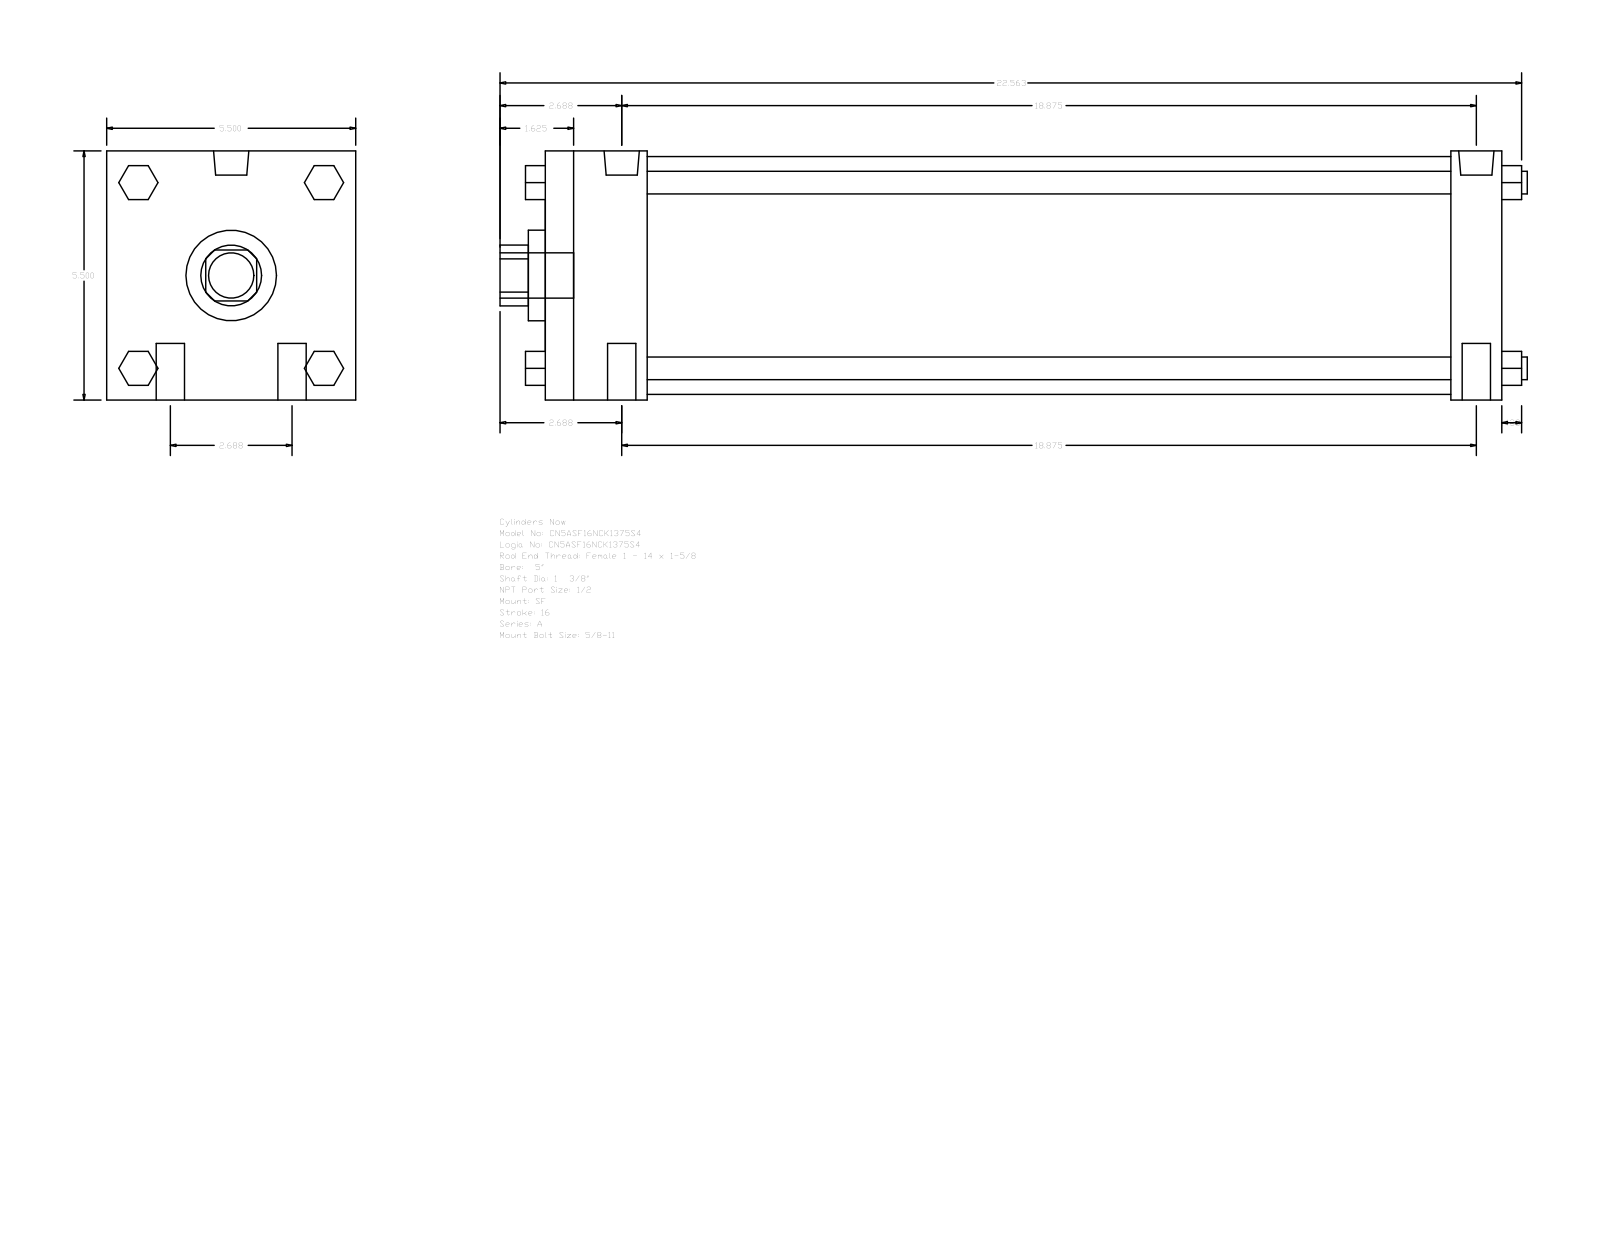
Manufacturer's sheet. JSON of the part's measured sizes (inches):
{"part_name": "A_SF__0500_1.375", "step_written_by": "GSSL Pune (CONFIG_CONTROL_DESIGN)", "units": "inches", "bodies": {"solids": 0, "faces": 124, "planar": 94, "cylindrical": 30, "other": 0}, "overall_size": [22.687, 5.5, 5.5], "round_holes": [[1.375, 1], [2, 1], [5.25, 1]], "round_bosses_or_shafts": [[0.625, 4], [0.5, 4], [0.778, 2], [0.344, 2], [1, 1]], "partial_cylinders_radius": [[0.672, 1]], "face_to_face_distances": [5.5, 21.125, 1.125, 2.25, 20, 17.75, 18.875, 0.75, 2.05, 3.55]}
